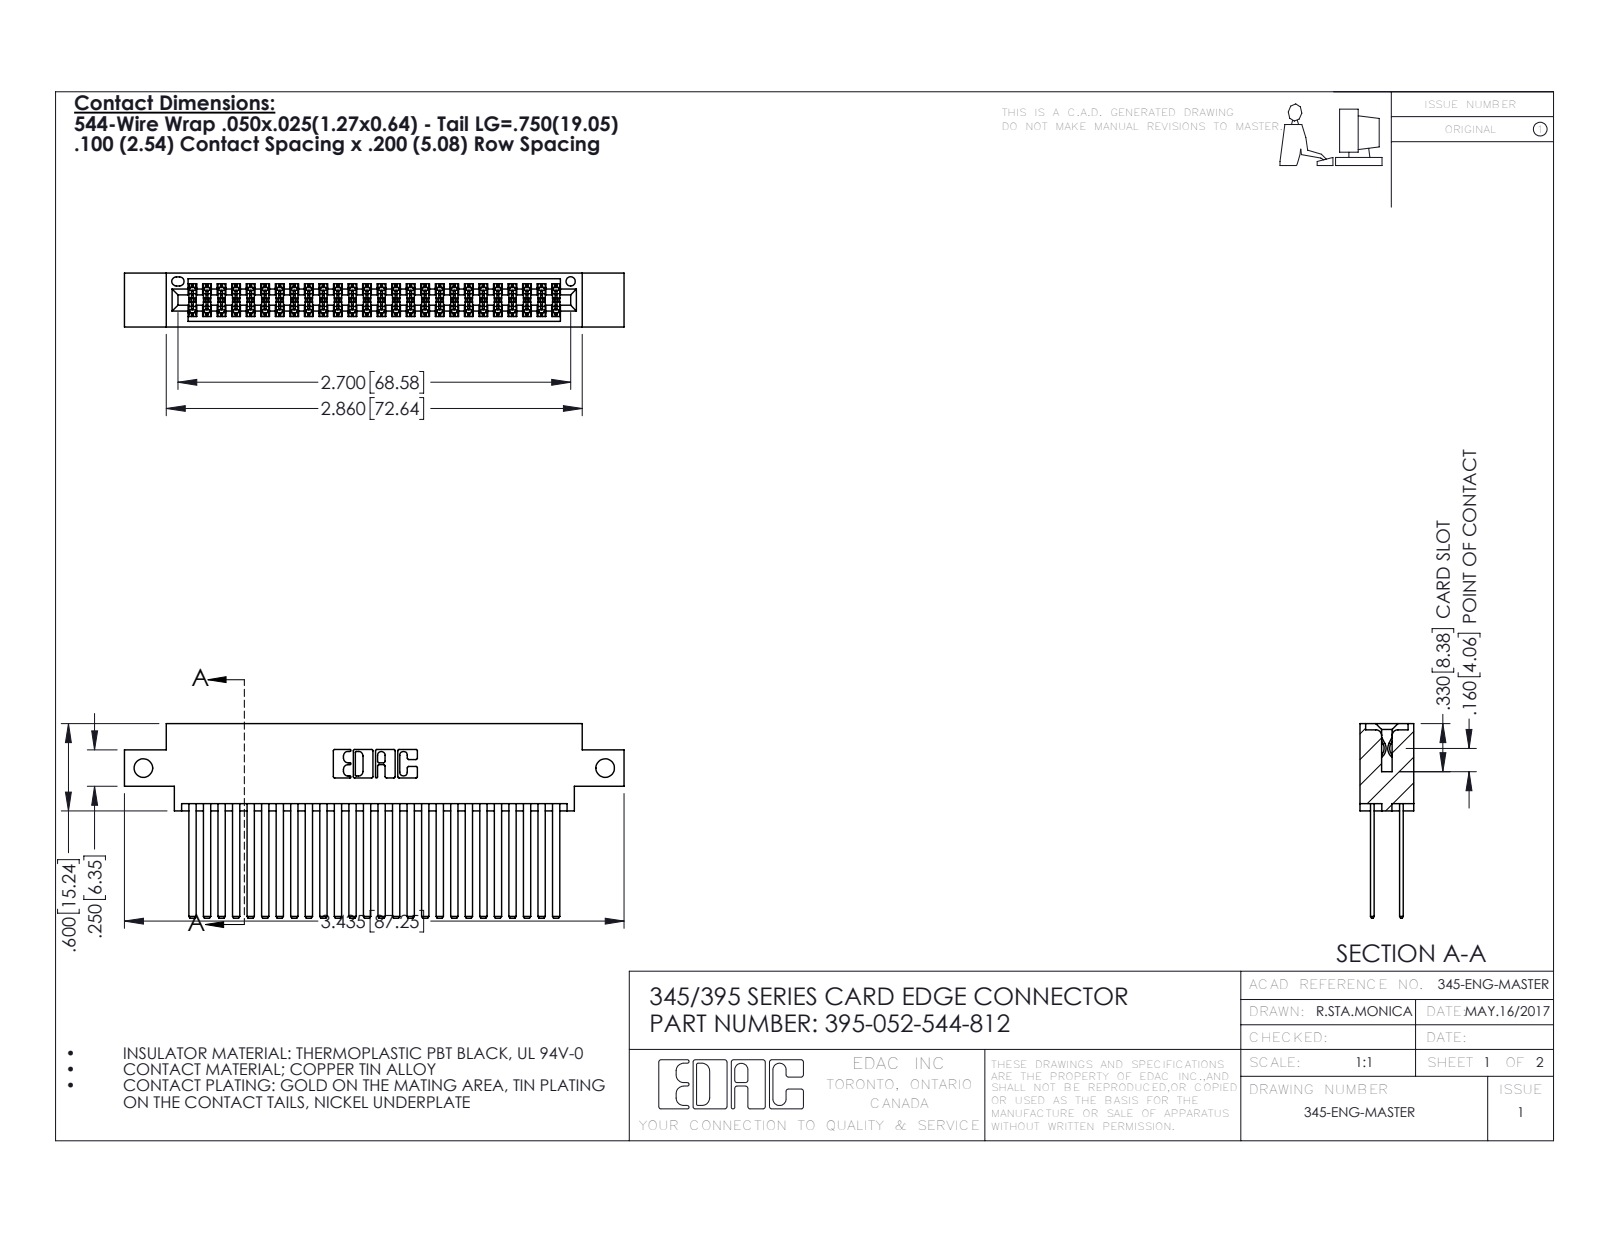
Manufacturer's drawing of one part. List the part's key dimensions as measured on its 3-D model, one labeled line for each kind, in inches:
Part name (STEP PRODUCT): 395-052-544-812; 345 Part_0.170 Offset - Side Mount; 345-292-001_345-293-144
STEP written by: SolidWorks 2016 (CONFIG_CONTROL_DESIGN)
Units: inches
Bodies: 53 solids, 2418 faces (1592 planar, 826 cylindrical, 0 other)
Overall size (bounding box): 3.435 × 1.337 × 0.37
Volume: 0.54 in³ · Surface area: 23.13 in²
Round holes (diameter × count): ⌀0.128 ×2, ⌀0.064 ×1
Partial cylindrical surfaces — rounded edges, fillets, slot ends (radius × count): R0.006 ×78, R0.01 ×22, R0.007 ×6, R0.031 ×6, R0.026 ×3, R0.014 ×2, R0.019 ×2, R0.022 ×2
Main face-to-face distances: 0.2, 0.025, 0.298, 0.072, 0.098, 0.272, 0.225, 0.175, 0.37, 0.15
Hole centre spacings: 3.175
